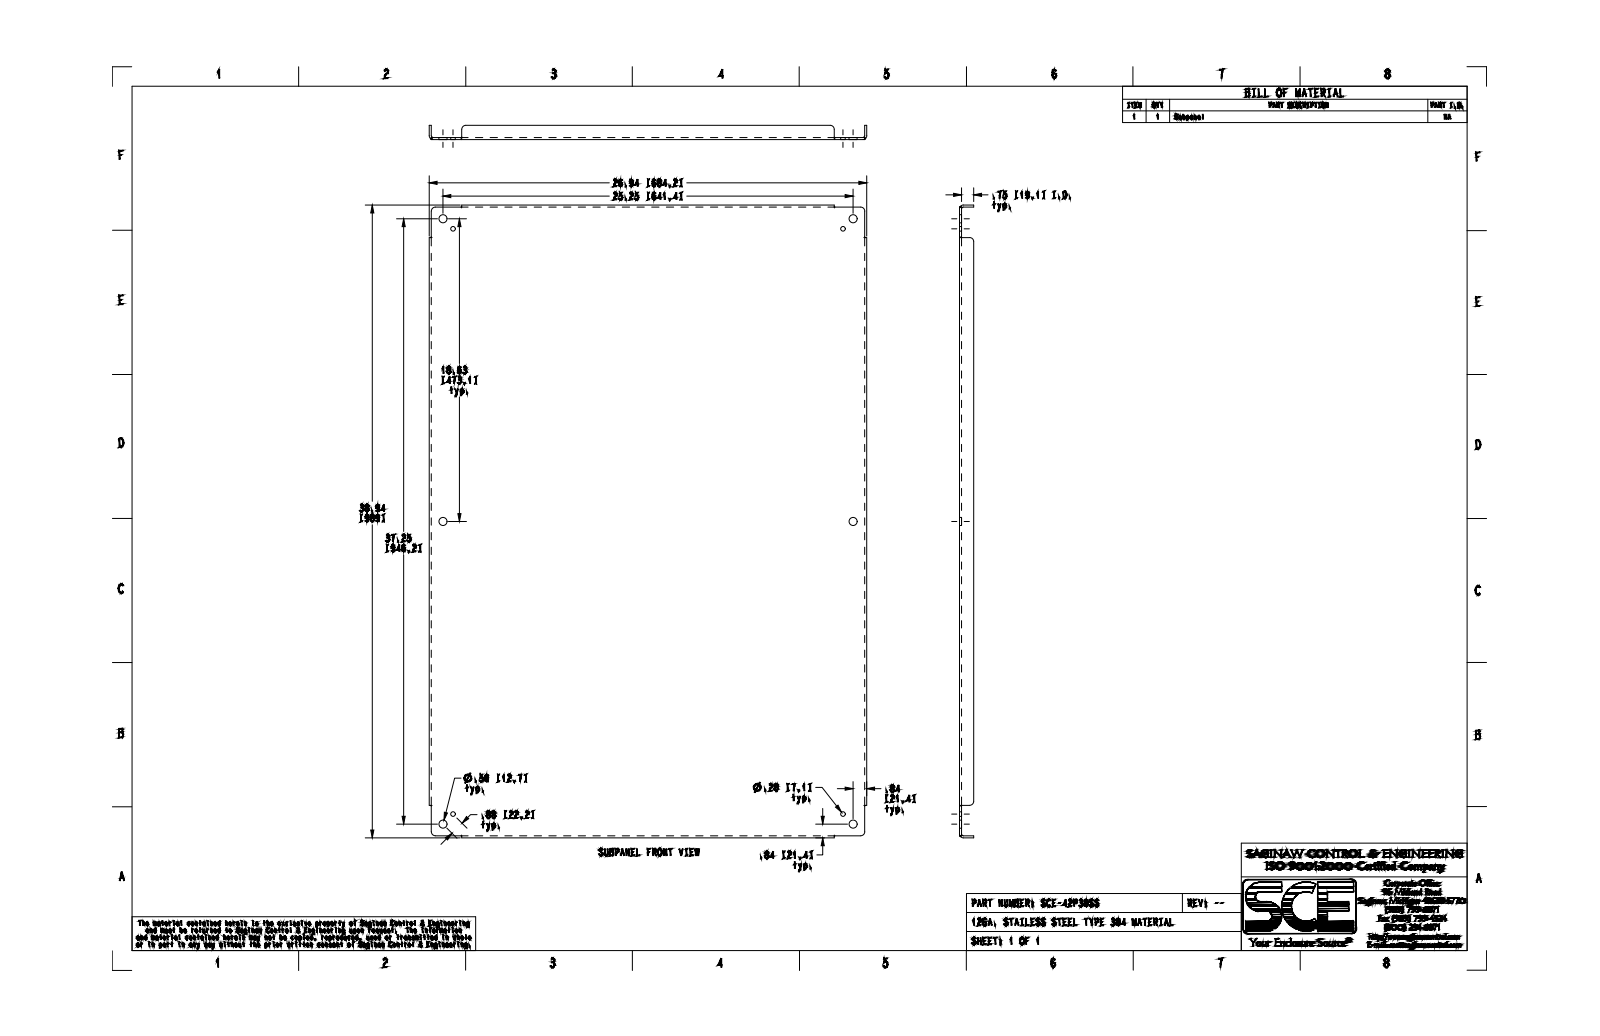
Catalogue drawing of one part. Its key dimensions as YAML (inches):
part_name: "SCE-42P30SS"
step_written_by: "SolidWorks 2019 (CONFIG_CONTROL_DESIGN)"
units: inches
bodies: {solids: 1, faces: 84, planar: 30, cylindrical: 30, other: 24}
overall_size: [38.938, 26.938, 0.875]
volume: 140.4
surface_area: 2266
round_holes:
  - {diameter: 0.5, count: 6}
  - {diameter: 0.281, count: 4}
partial_cylinders:
  - {radius: 0.25, count: 8}
  - {radius: 0.112, count: 4}
  - {radius: 0.237, count: 4}
face_to_face_distances: [0.125, 0.125, 26.813, 38.813, 26.687, 26.938, 38.687, 38.938, 0.75, 0.875]
hole_center_spacings: [0.875, 18.017, 18.625, 24.639, 30.511, 31.376, 36.636, 44.142]
